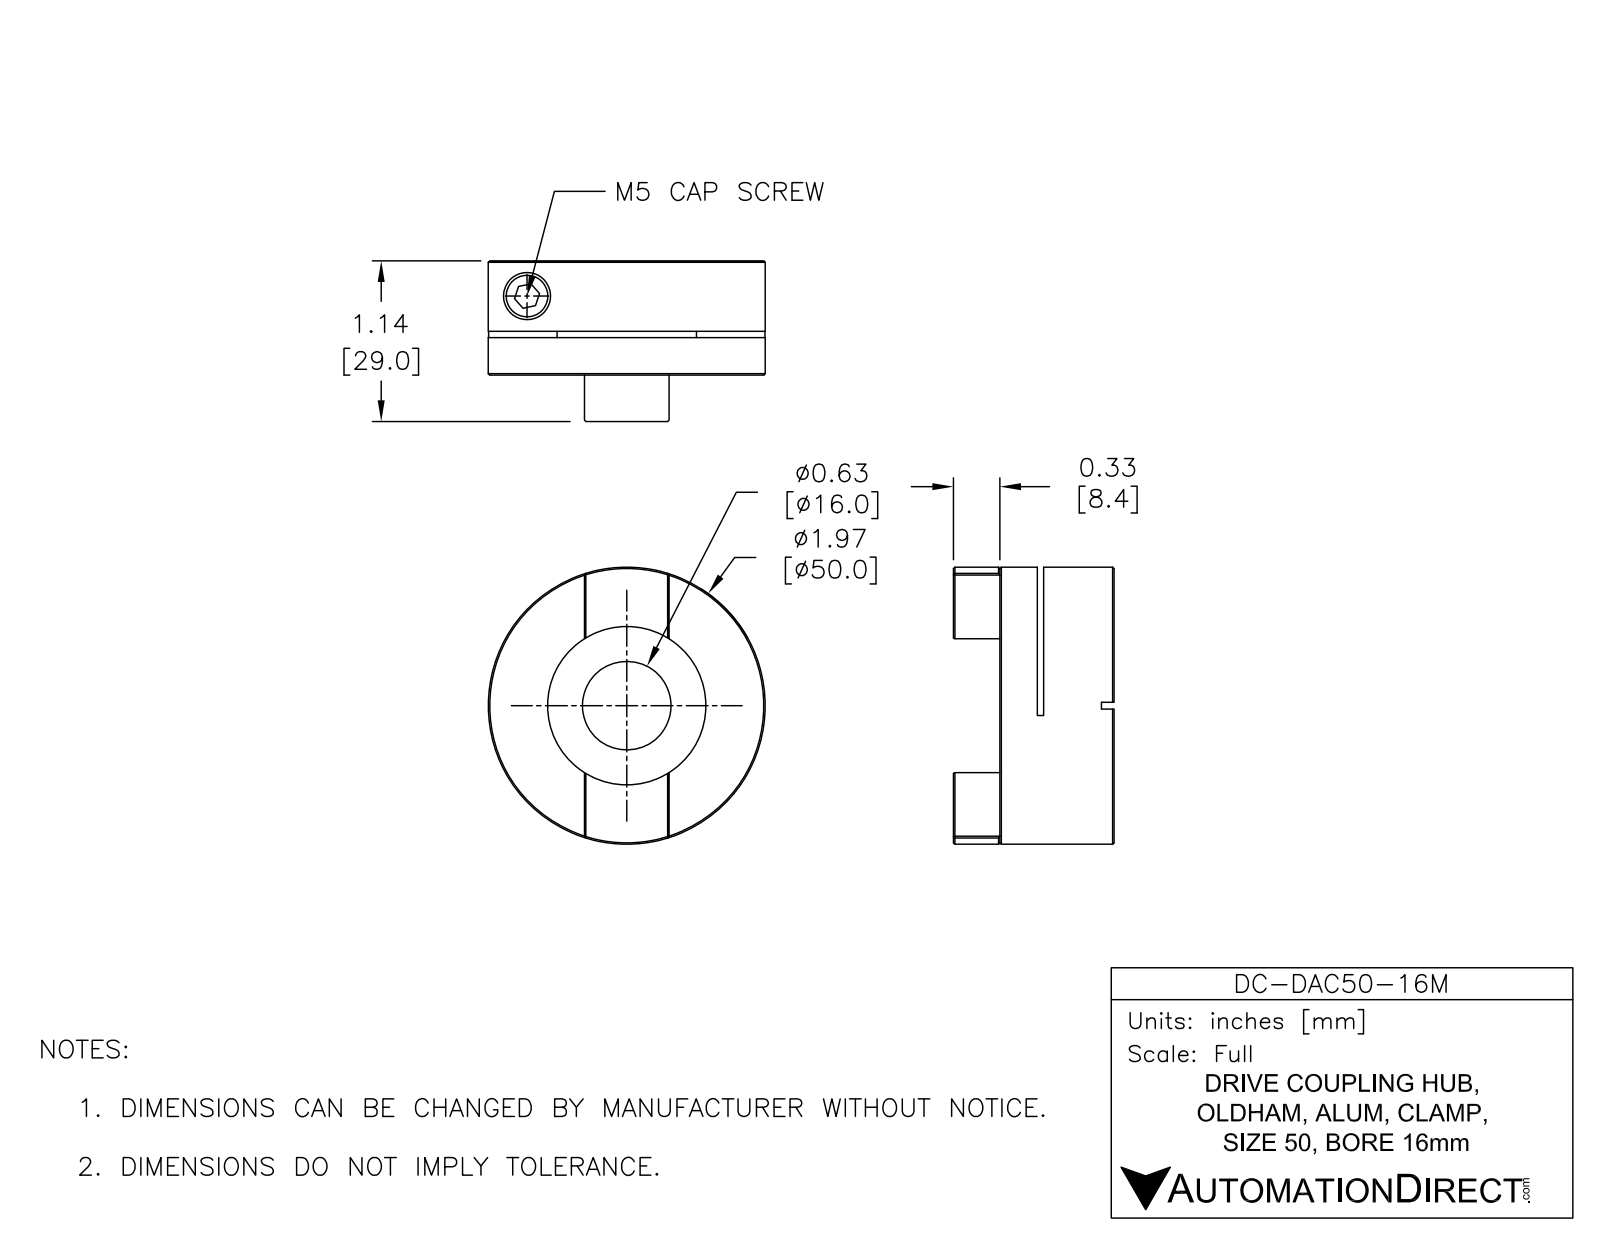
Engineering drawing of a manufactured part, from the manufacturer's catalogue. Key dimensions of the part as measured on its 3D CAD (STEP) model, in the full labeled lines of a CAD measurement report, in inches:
Part name (STEP PRODUCT): DC-DAC50-16M
STEP written by: SolidWorks 2015 (AUTOMOTIVE_DESIGN)
Units: inches
Bodies: 1 solid, 57 faces (30 planar, 17 cylindrical, 10 other)
Overall size (bounding box): 1.969 × 1.969 × 1.141
Volume: 2.15 in³ · Surface area: 18.29 in²
Round holes (diameter × count): ⌀0.217 ×1, ⌀0.394 ×1, ⌀0.63 ×1, ⌀1.125 ×1
Round bosses / shafts (diameter × count): ⌀1.969 ×1
Partial cylindrical surfaces — rounded edges, fillets, slot ends (radius × count): R1 ×1
Main face-to-face distances: 0.811, 0.545, 0.266, 0.5, 0.045, 0.311, 0.741, 0.241, 0.196, 0.07
